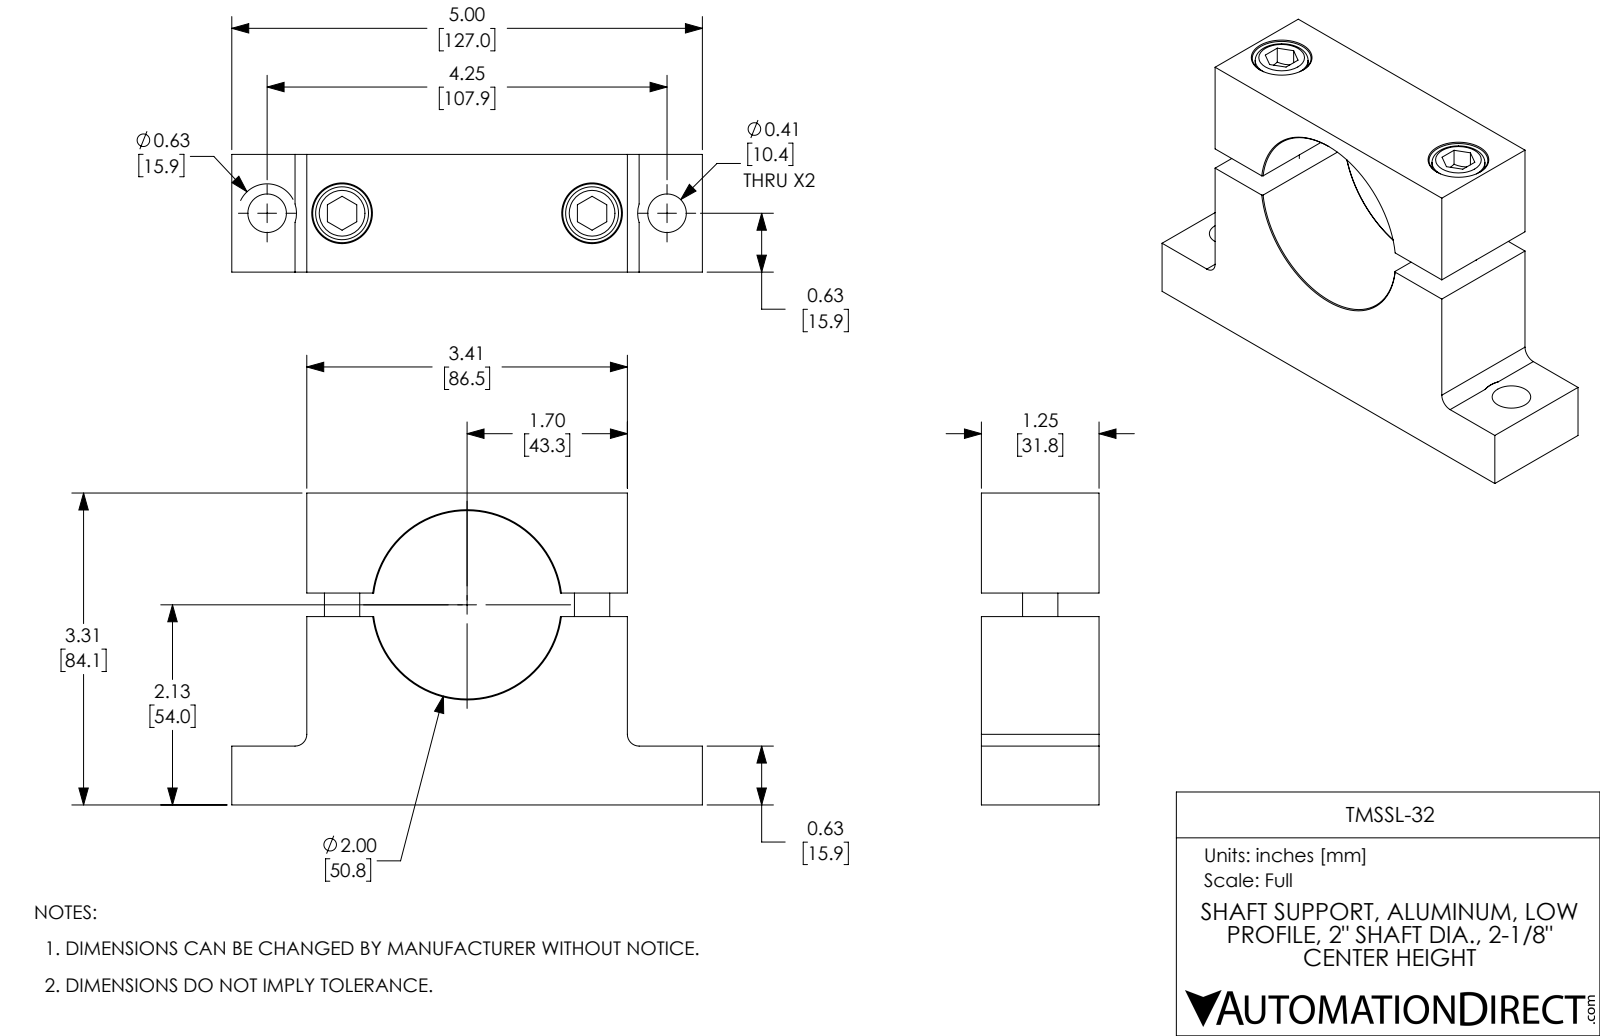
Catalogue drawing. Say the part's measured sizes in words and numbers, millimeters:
The part is named "TMSSL-32". Its 3-D file was written by "SolidWorks 2017 (AUTOMOTIVE_DESIGN)". It is 4 solids with 92 faces: 38 planar, 30 cylindrical and 24 other. Overall it measures 127 by 84.1 by 31.8 millimeters. Its volume is 173 700 cubic millimeters and its surface area 39 860 square millimeters. Round holes: 2 of diameter 7.8, 2 of diameter 10.1, 2 of diameter 10.4, 2 of diameter 15.9, 1 of diameter 50.8. Round bosses or shafts: 2 of diameter 14.3, 1 of diameter 9.5, 1 of diameter 9.5. Partial cylindrical surfaces (rounded edges, fillets, slot ends): 2 of radius 3.2, 2 of radius 8. The main face-to-face distances are 31.8, 84.1, 86.5, 50.8, 33.3, 20.2, 106.8, 57.2, 6.4, 27. The hole center spacings are 20.2, 87.7, 67.5, 107.9.
